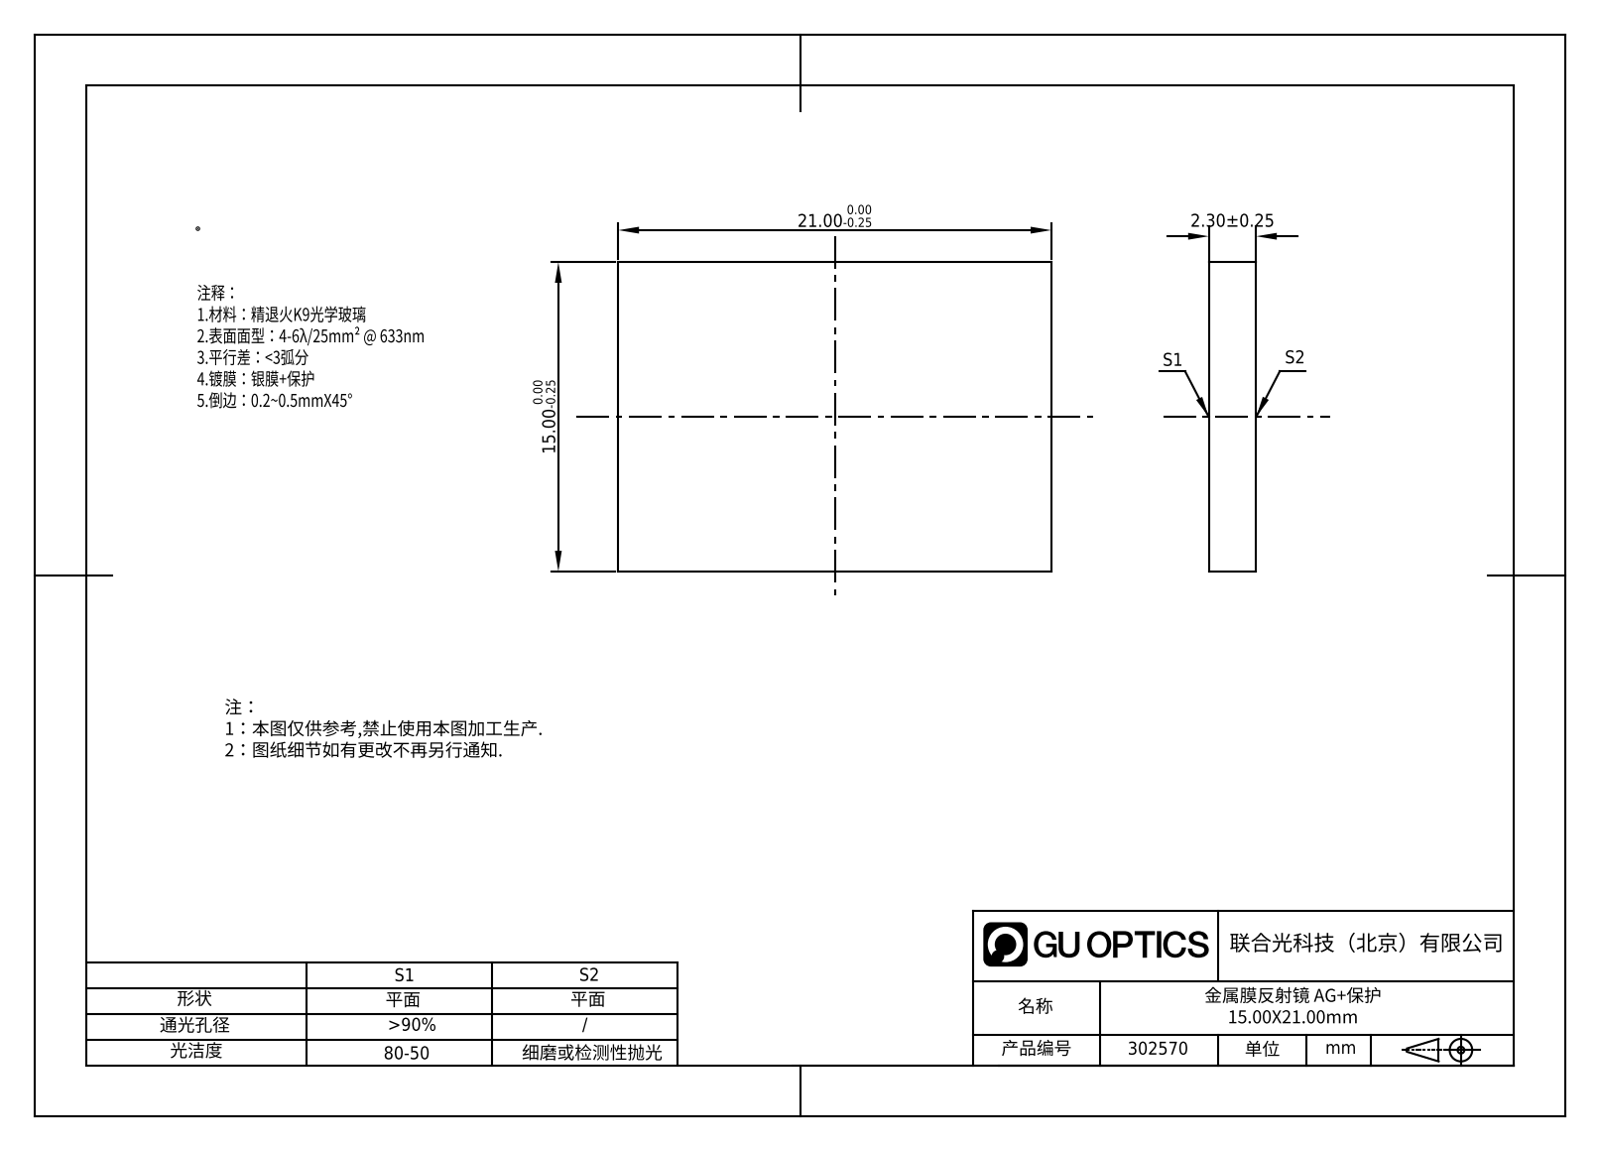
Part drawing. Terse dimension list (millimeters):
name: 302512
written by: SolidWorks 2016 (AUTOMOTIVE_DESIGN)
unit: mm
bodies: 1 solid, 6 faces (6 planar, 0 cylindrical, 0 other)
size: 21 × 15 × 2.3
volume: 724 mm³; area: 796 mm²
face distances: 2.3, 15, 21
